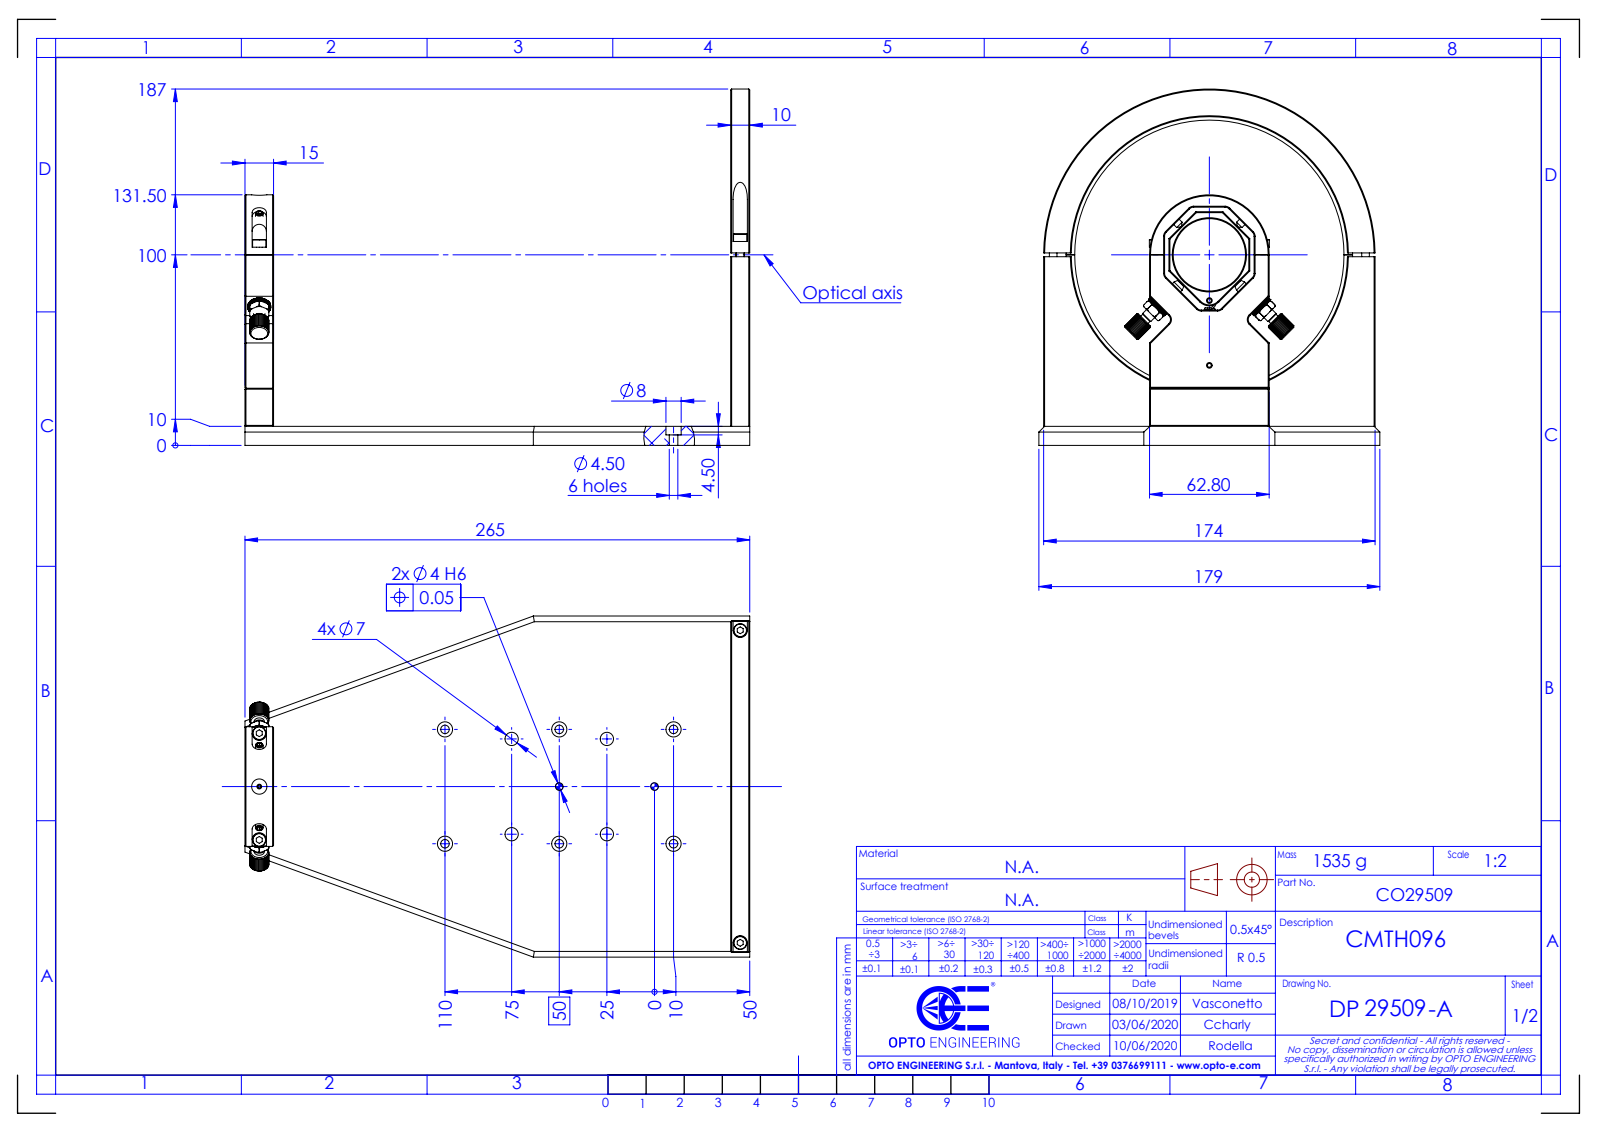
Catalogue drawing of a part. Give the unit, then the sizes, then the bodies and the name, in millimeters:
Units: millimetres
Overall size (bounding box): 265 × 187 × 179
Round holes (diameter × count): ⌀8 ×11, ⌀4.5 ×6, ⌀7 ×4, ⌀3 ×2, ⌀4 ×2, ⌀2.5 ×1, ⌀10.5 ×1, ⌀38 ×1, ⌀145 ×1
Round bosses / shafts (diameter × count): ⌀7 ×6, ⌀6 ×2, ⌀5.4 ×2, ⌀4 ×2
Partial cylindrical surfaces — rounded edges, fillets, slot ends (radius × count): R0.1 ×14, R3 ×10, R3.75 ×6, R6 ×2, R7 ×1, R31.4 ×1, R87 ×1
Main face-to-face distances: 10, 265, 255, 15, 250, 240, 2.33, 7.67, 2.5, 55.6
Hole centre spacings: 35.36, 60, 50, 25.5, 60.42, 65.19, 67.08, 84.85
Bodies: 0 solids, 699 faces (421 planar, 152 cylindrical, 126 other)
Part name (STEP PRODUCT): DP29509
STEP written by: SolidWorks 2021 (CONFIG_CONTROL_DESIGN)
